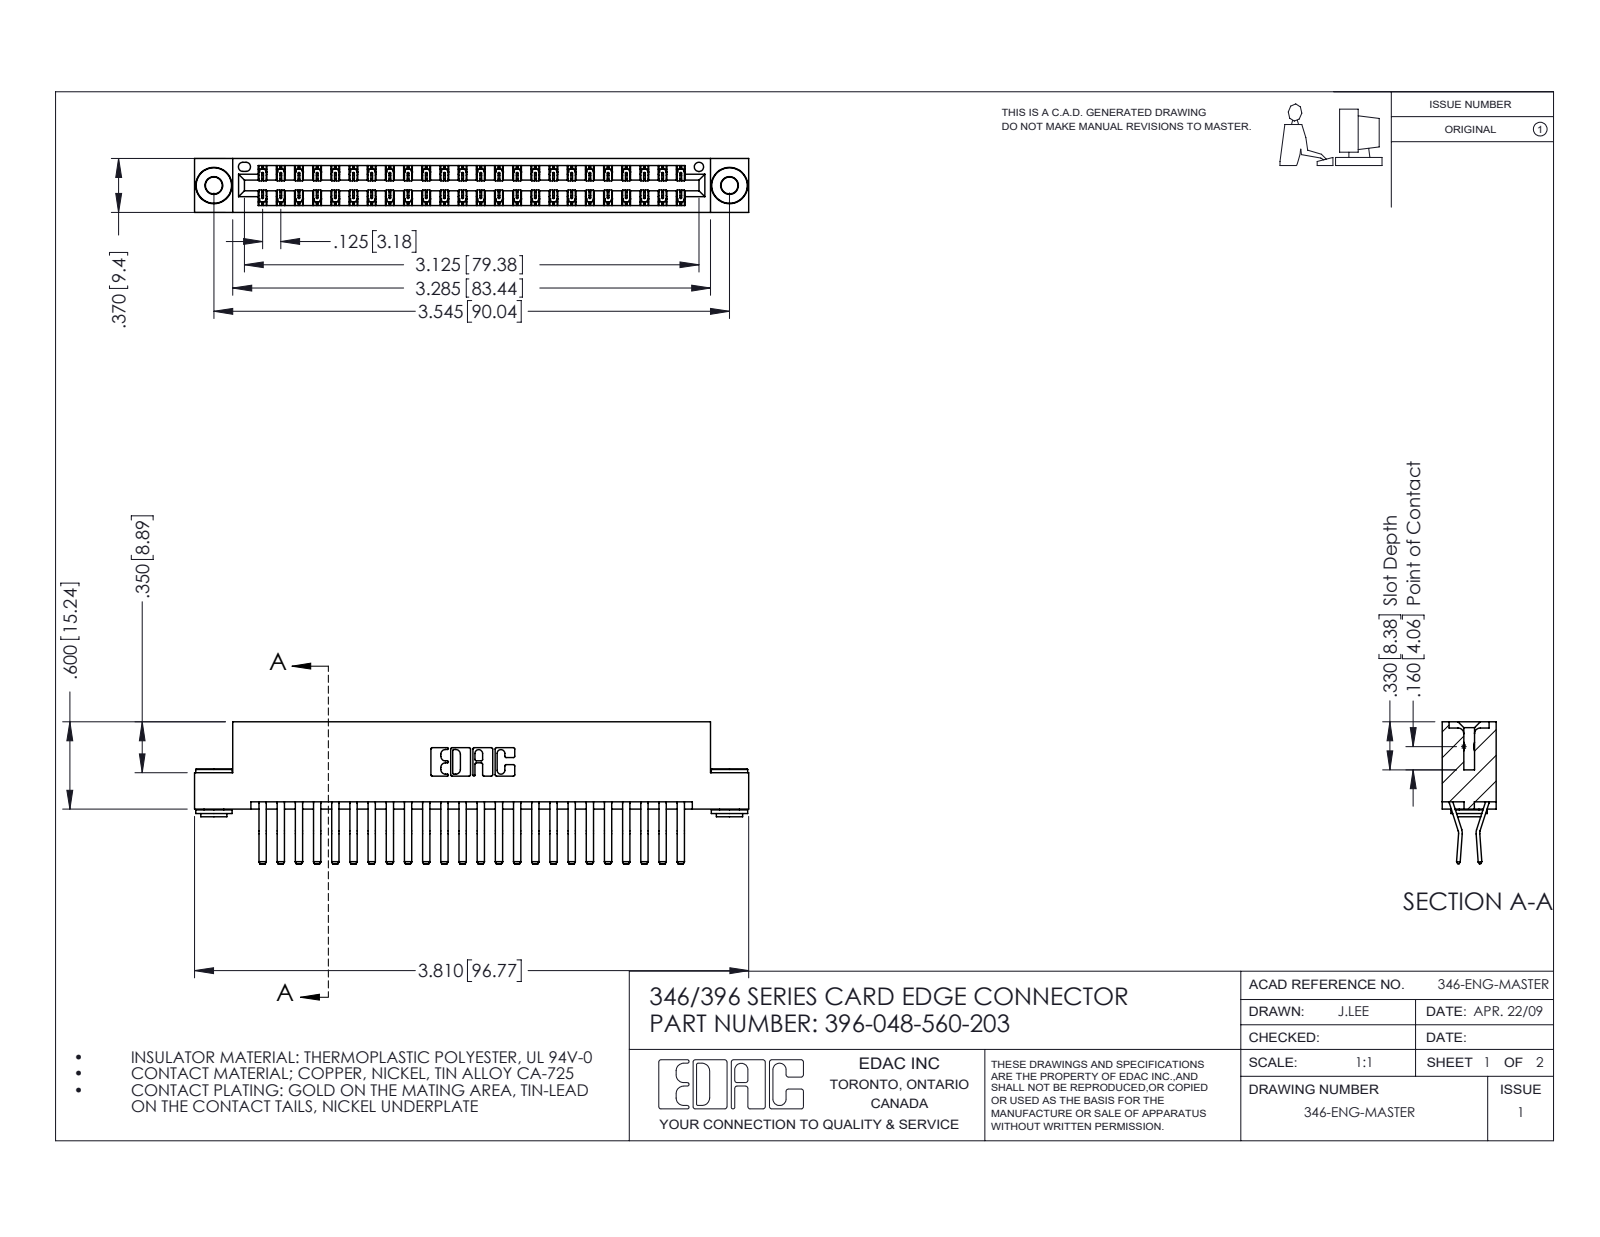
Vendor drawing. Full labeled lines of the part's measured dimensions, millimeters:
Part name (STEP PRODUCT): 346 Part_Flush Mounting Lugs - 0.156 Dia-TH; 396-048-560-203; 345-250-002_345-250-002-102; 345-292-001_560 Tail
STEP written by: SolidWorks 2016 (CONFIG_CONTROL_DESIGN)
Units: millimetres
Bodies: 51 solids, 2752 faces (1766 planar, 978 cylindrical, 8 other)
Overall size (bounding box): 96.8 × 24.8 × 9.4
Volume: 9 640 mm³ · Surface area: 14 010 mm²
Round holes (diameter × count): ⌀2.9 ×2, ⌀4 ×2, ⌀1.6 ×1
Round bosses / shafts (diameter × count): ⌀6.4 ×2, ⌀4.6 ×2, ⌀3.5 ×2
Partial cylindrical surfaces — rounded edges, fillets, slot ends (radius × count): R0.2 ×72, R0.3 ×22, R0.2 ×6, R0.8 ×6, R0.7 ×3, R0.3 ×2, R0.4 ×2, R0.6 ×2
Main face-to-face distances: 1.2, 8.2, 6.4, 9.4, 0.6, 1.8, 7.6, 7, 3.8, 5.6
Hole centre spacings: 6.2, 84.8, 90
